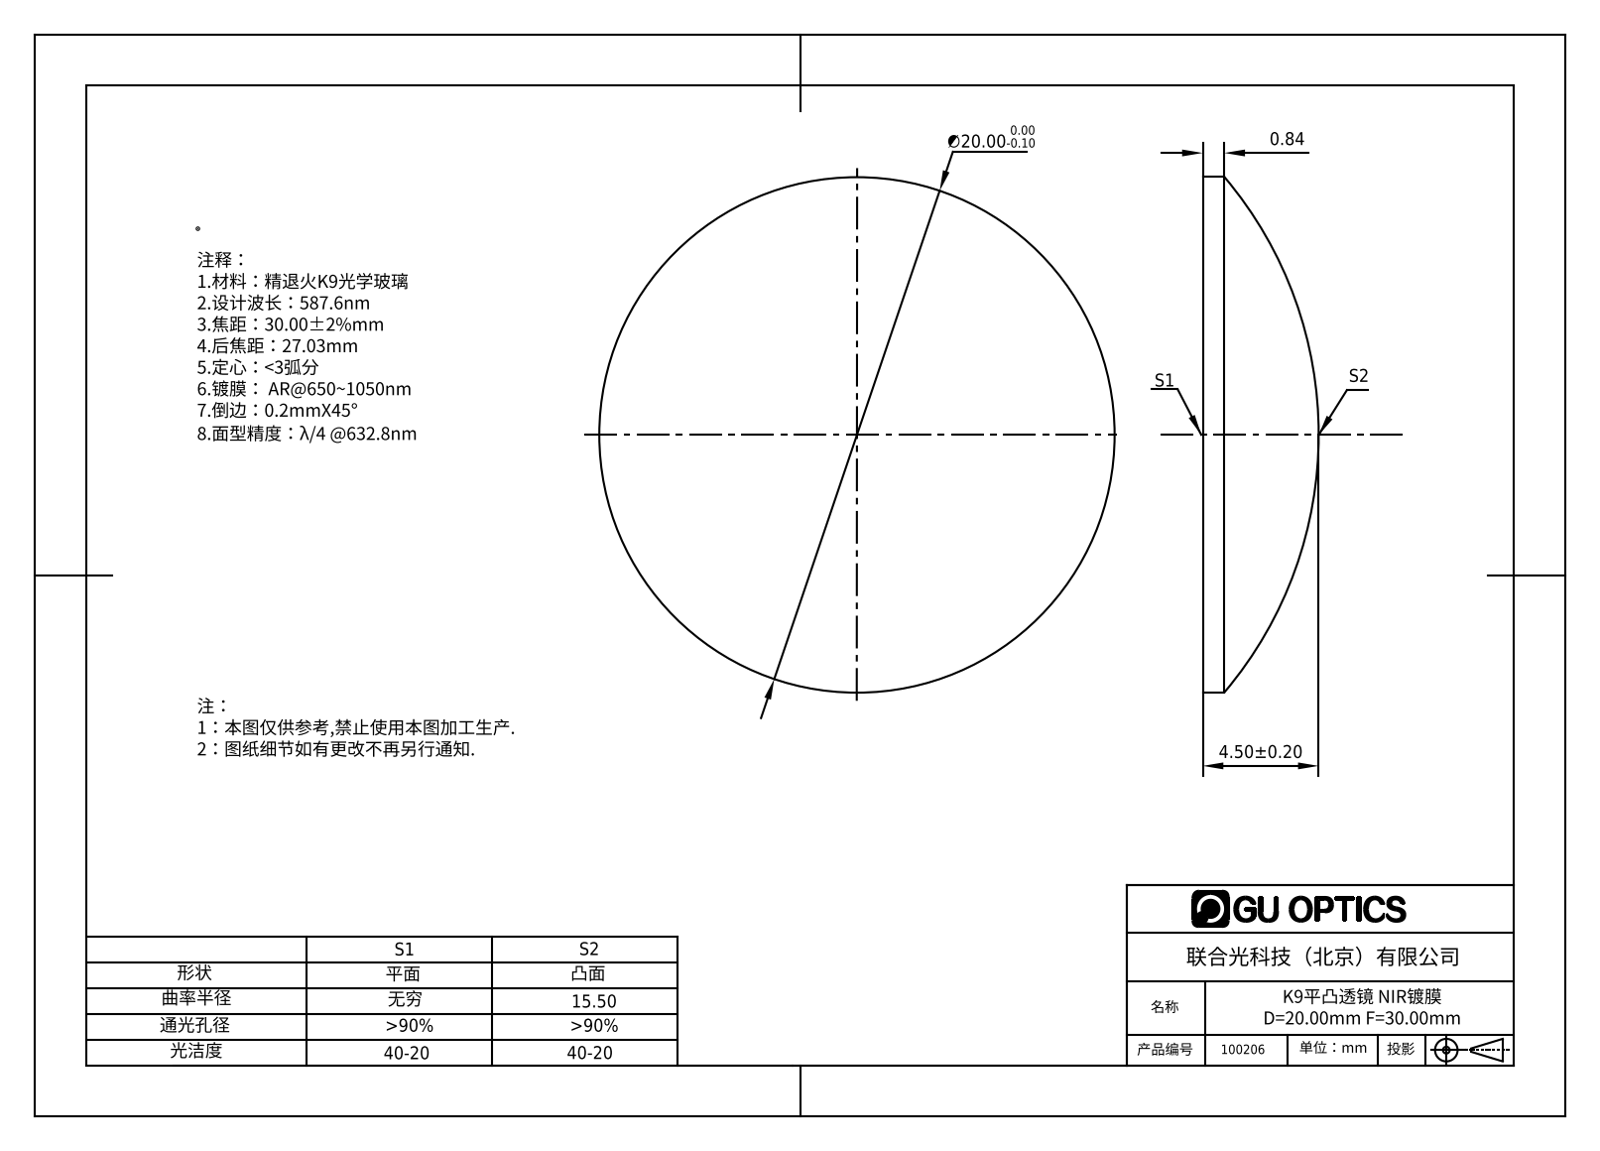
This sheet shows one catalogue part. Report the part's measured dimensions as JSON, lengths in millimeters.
{"part_name": "100206", "step_written_by": "SolidWorks 2016 (AUTOMOTIVE_DESIGN)", "units": "millimeters", "bodies": {"solids": 1, "faces": 5, "planar": 1, "cylindrical": 2, "other": 2}, "overall_size": [20, 20, 4.5], "volume_mm3": 864, "surface_area_mm2": 723, "round_bosses_or_shafts": [[20, 1]]}
